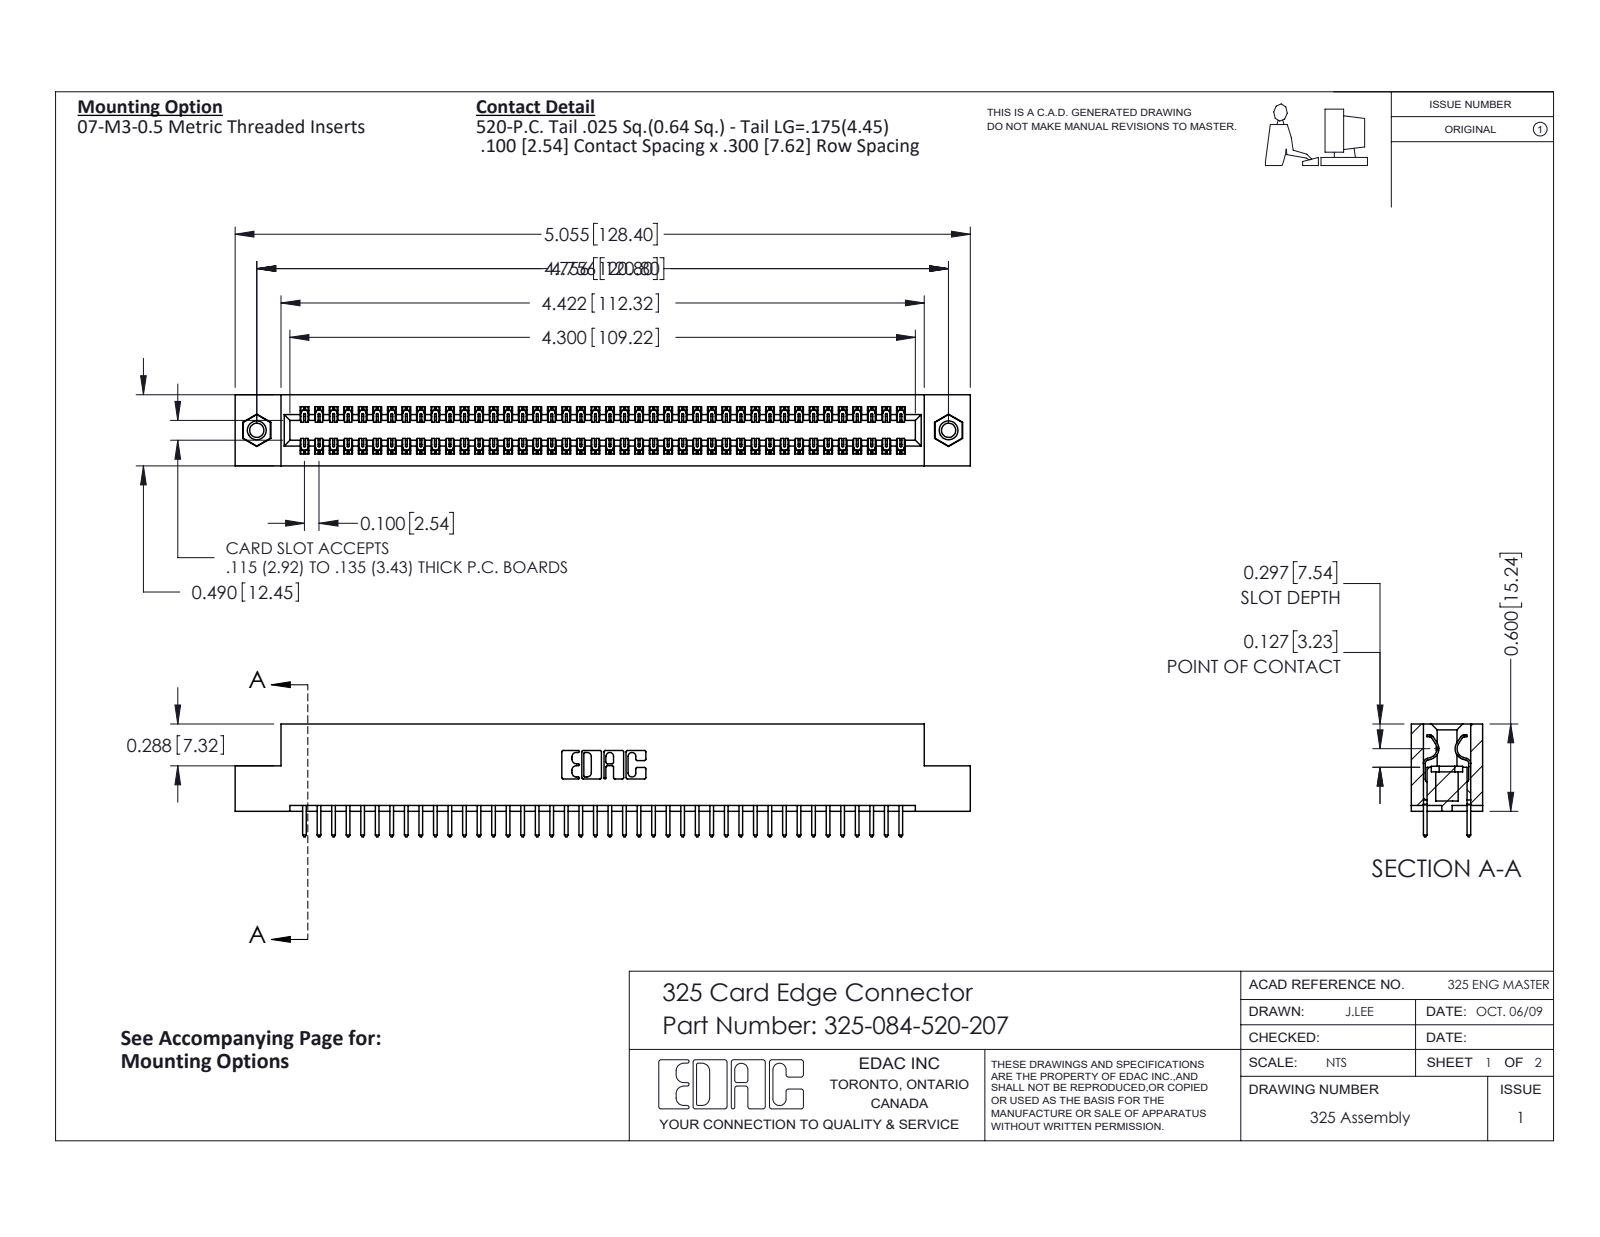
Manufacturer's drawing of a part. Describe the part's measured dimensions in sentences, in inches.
The part is named "325 Part_TI; 325-084-520-207; 325-292-001_325-293-120; 345-250-001_345-250-005-103". Its 3-D file was written by "SolidWorks 2016 (CONFIG_CONTROL_DESIGN)". It is 87 solids with 4542 faces: 3126 planar, 1400 cylindrical and 16 other. Overall it measures 5.055 by 0.775 by 0.49 inches. Its volume is 1.01 cubic inches and its surface area 30.83 square inches. Round holes: 2 of diameter 0.098, 2 of diameter 0.125, 2 of diameter 0.16. Round bosses or shafts: 2 of diameter 0.155. Partial cylindrical surfaces (rounded edges, fillets, slot ends): 126 of radius 0.006, 84 of radius 0.01, 22 of radius 0.01, 6 of radius 0.007, 6 of radius 0.031, 3 of radius 0.026, 2 of radius 0.014, 2 of radius 0.022. The main face-to-face distances are 0.083, 0.407, 0.3, 0.49, 0.107, 0.383, 0.025, 0.325, 0.275, 0.56. The hole center spacings are 4.756.
